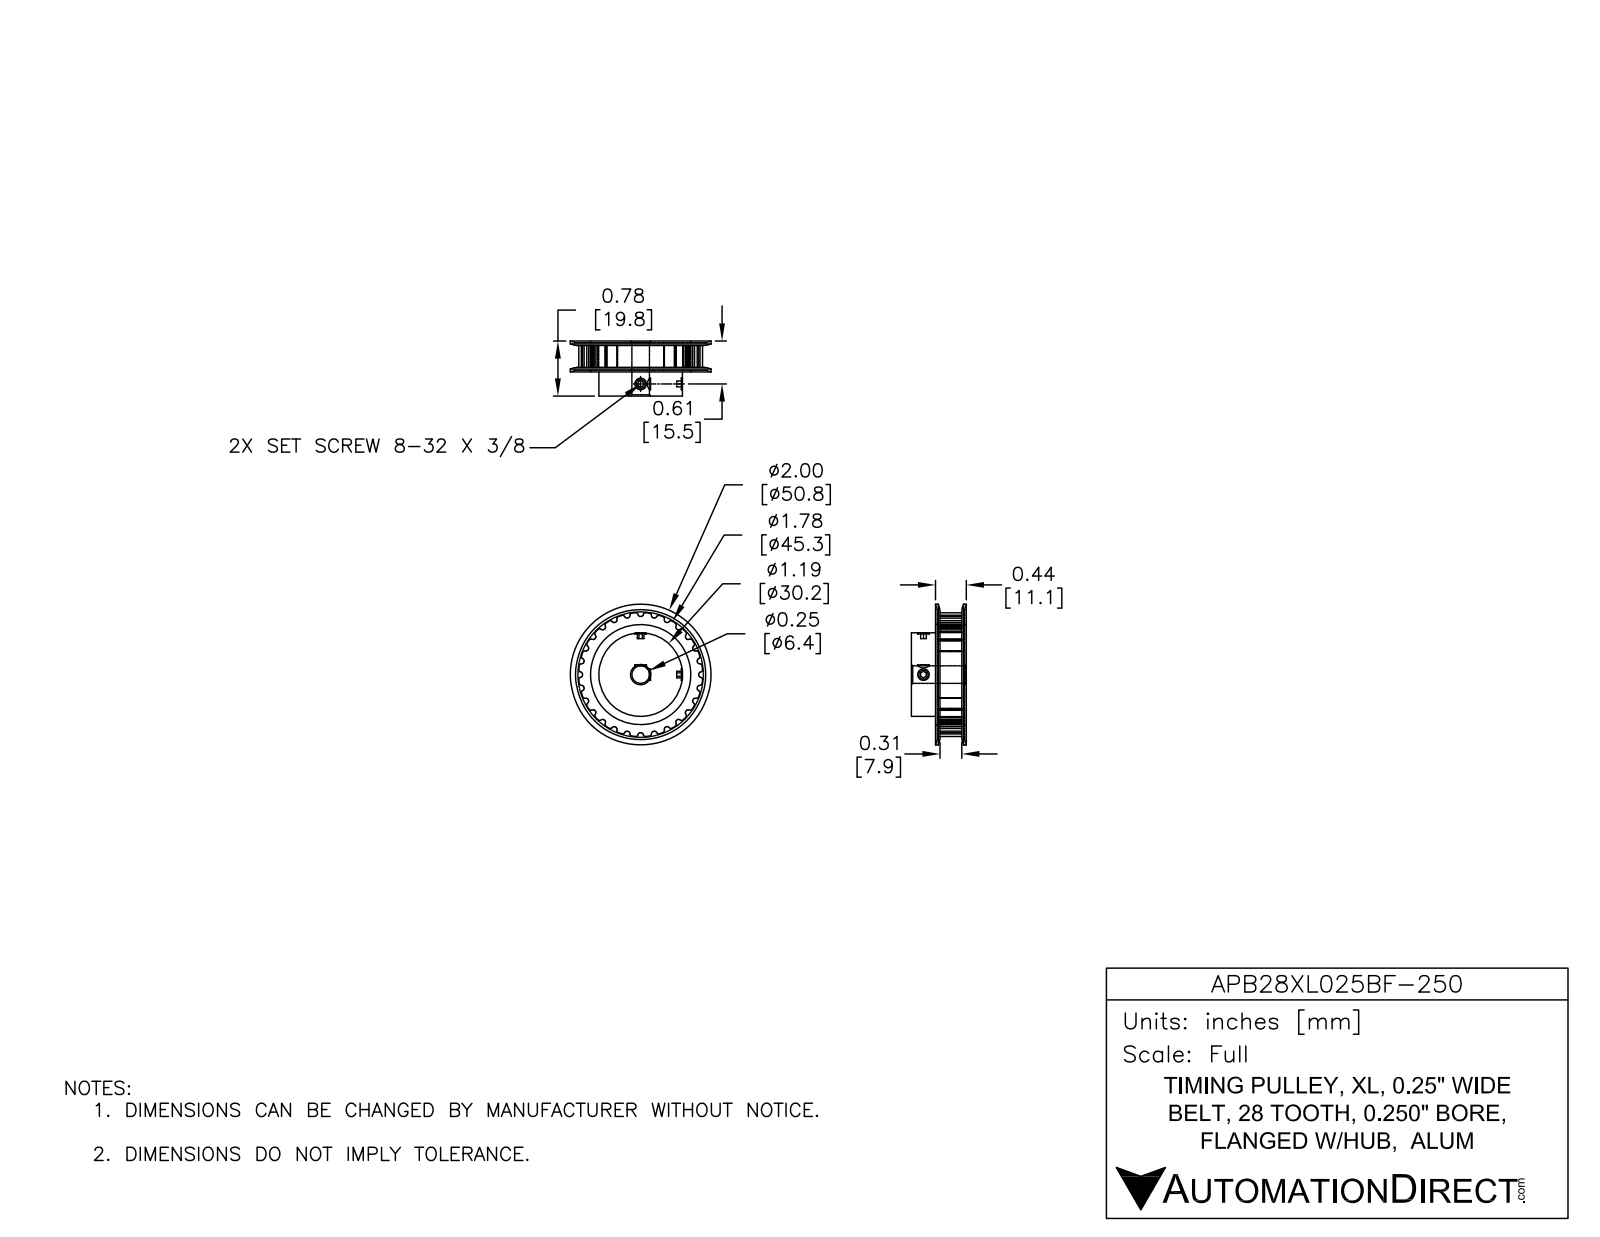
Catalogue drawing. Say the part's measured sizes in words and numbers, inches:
The part is named "APB28XL025BF-250". Its 3-D file was written by "SolidWorks 2014 (AUTOMOTIVE_DESIGN)". It is 1 solid with 282 faces: 90 planar, 170 cylindrical and 22 other. Overall it measures 2 by 2 by 0.781 inches. Its volume is 1.33 cubic inches and its surface area 12.76 square inches. Round holes: 2 of diameter 0.088, 1 of diameter 0.25. Round bosses or shafts: 1 of diameter 1.188. Partial cylindrical surfaces (rounded edges, fillets, slot ends): 112 of radius 0.015, 1 of radius 0.826. The main face-to-face distances are 0.375, 0.033, 0.407, 0.781, 0.748, 0.374, 0.032, 0.343, 1.763, 0.375.
